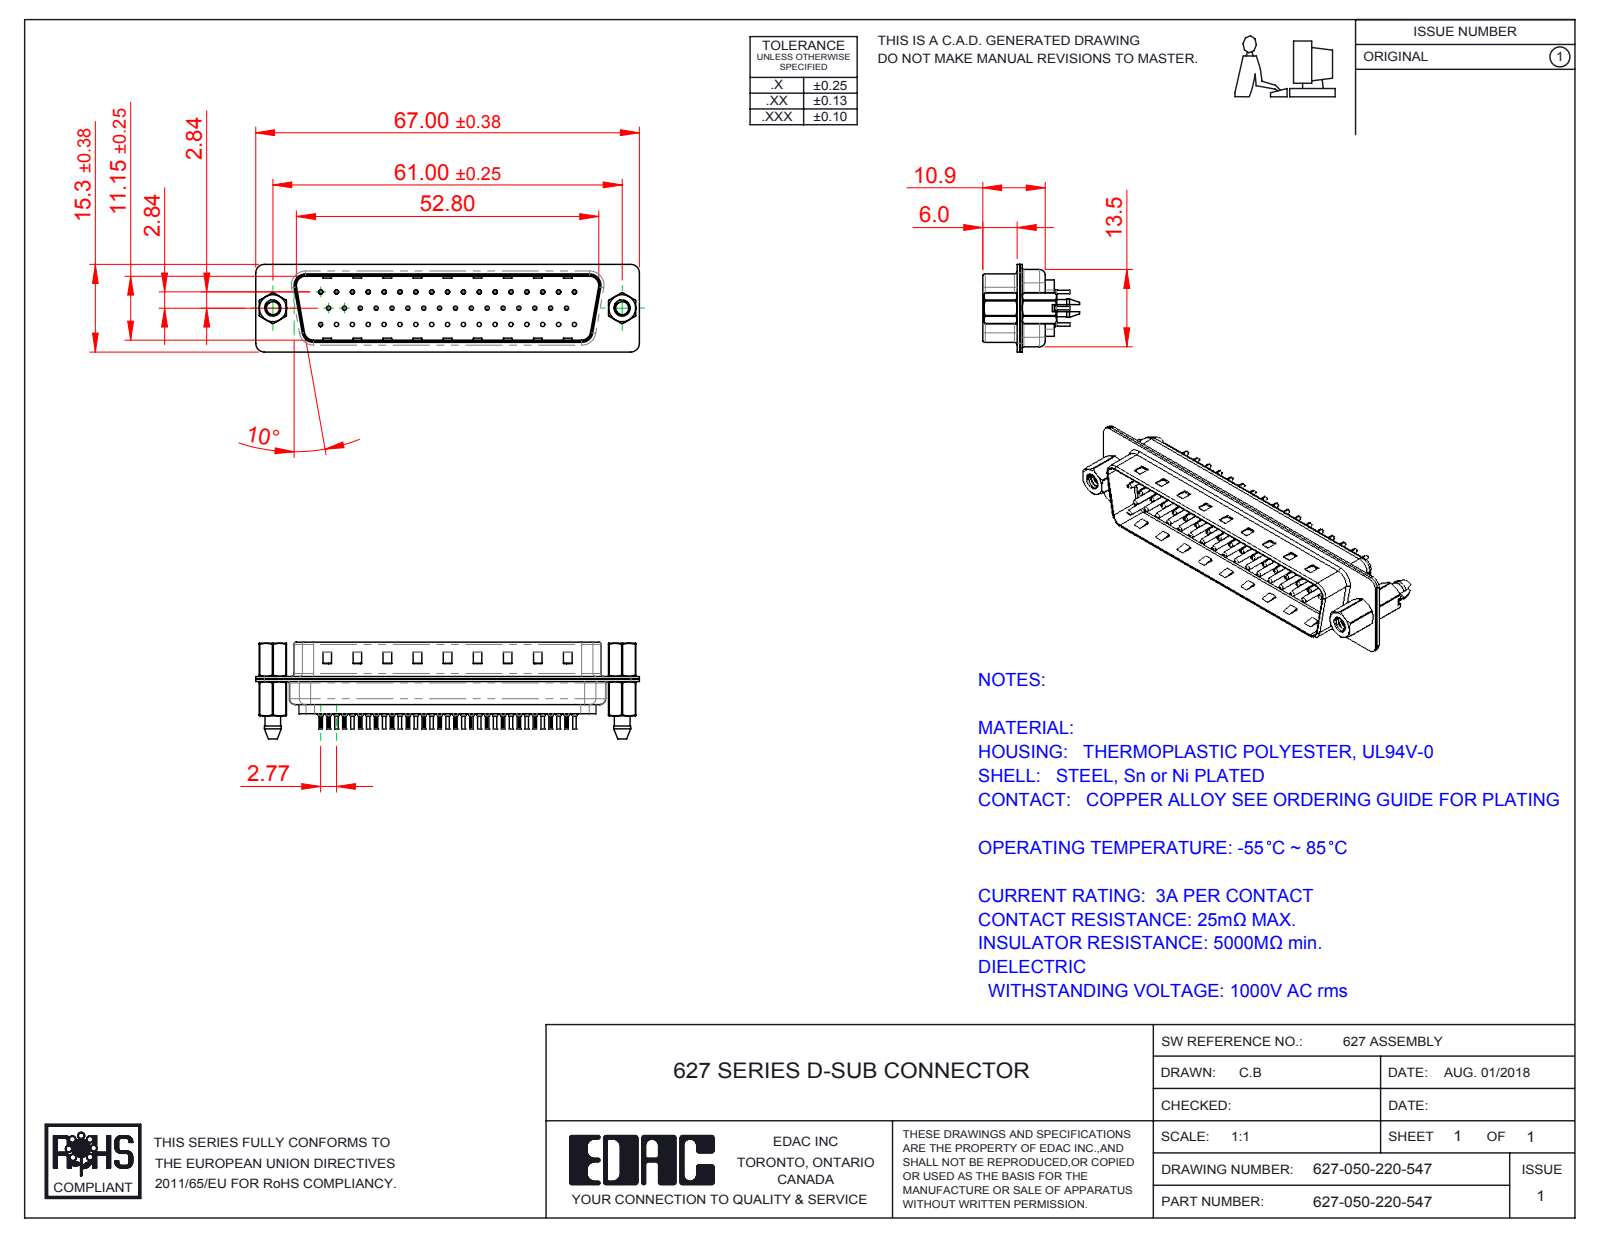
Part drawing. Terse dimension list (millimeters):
name: 627 Contact Row 2_20L; 627-050-220-547; 627 4-40 Threaded Boardlock_LP; 627 Housing_50 LP (+5 more)
written by: SolidWorks 2016 (CONFIG_CONTROL_DESIGN)
unit: mm
bodies: 41 solids, 4072 faces (1105 planar, 1599 cylindrical, 1368 other)
size: 67 × 16.9 × 15.3
volume: 4 604 mm³; area: 11 730 mm²
holes: 50× ⌀1.6, 34× ⌀0.2, 34× ⌀0.35, 34× ⌀1.1, 16× ⌀0.75, 16× ⌀2, 2× ⌀2.26, 2× ⌀2.29, 2× ⌀4, 2× ⌀4.8
bosses: 34× ⌀2, 34× ⌀1.5, 34× ⌀0.75, 34× ⌀0.6, 2× ⌀4.9, 2× ⌀2.79
rounds: 68× R0.1, 18× R1.5, 12× R2, 10× R1.6, 8× R0.5, 4× R0.25, 4× R0.6, 4× R0.65
face distances: 0.4, 0.45, 11.55, 0.9, 6.05, 6.5, 12.33, 0.78, 0.77, 12.32
hole spacings: 3.16, 2.77, 5.54, 8.31, 11.08, 13.85, 16.62, 5.03
